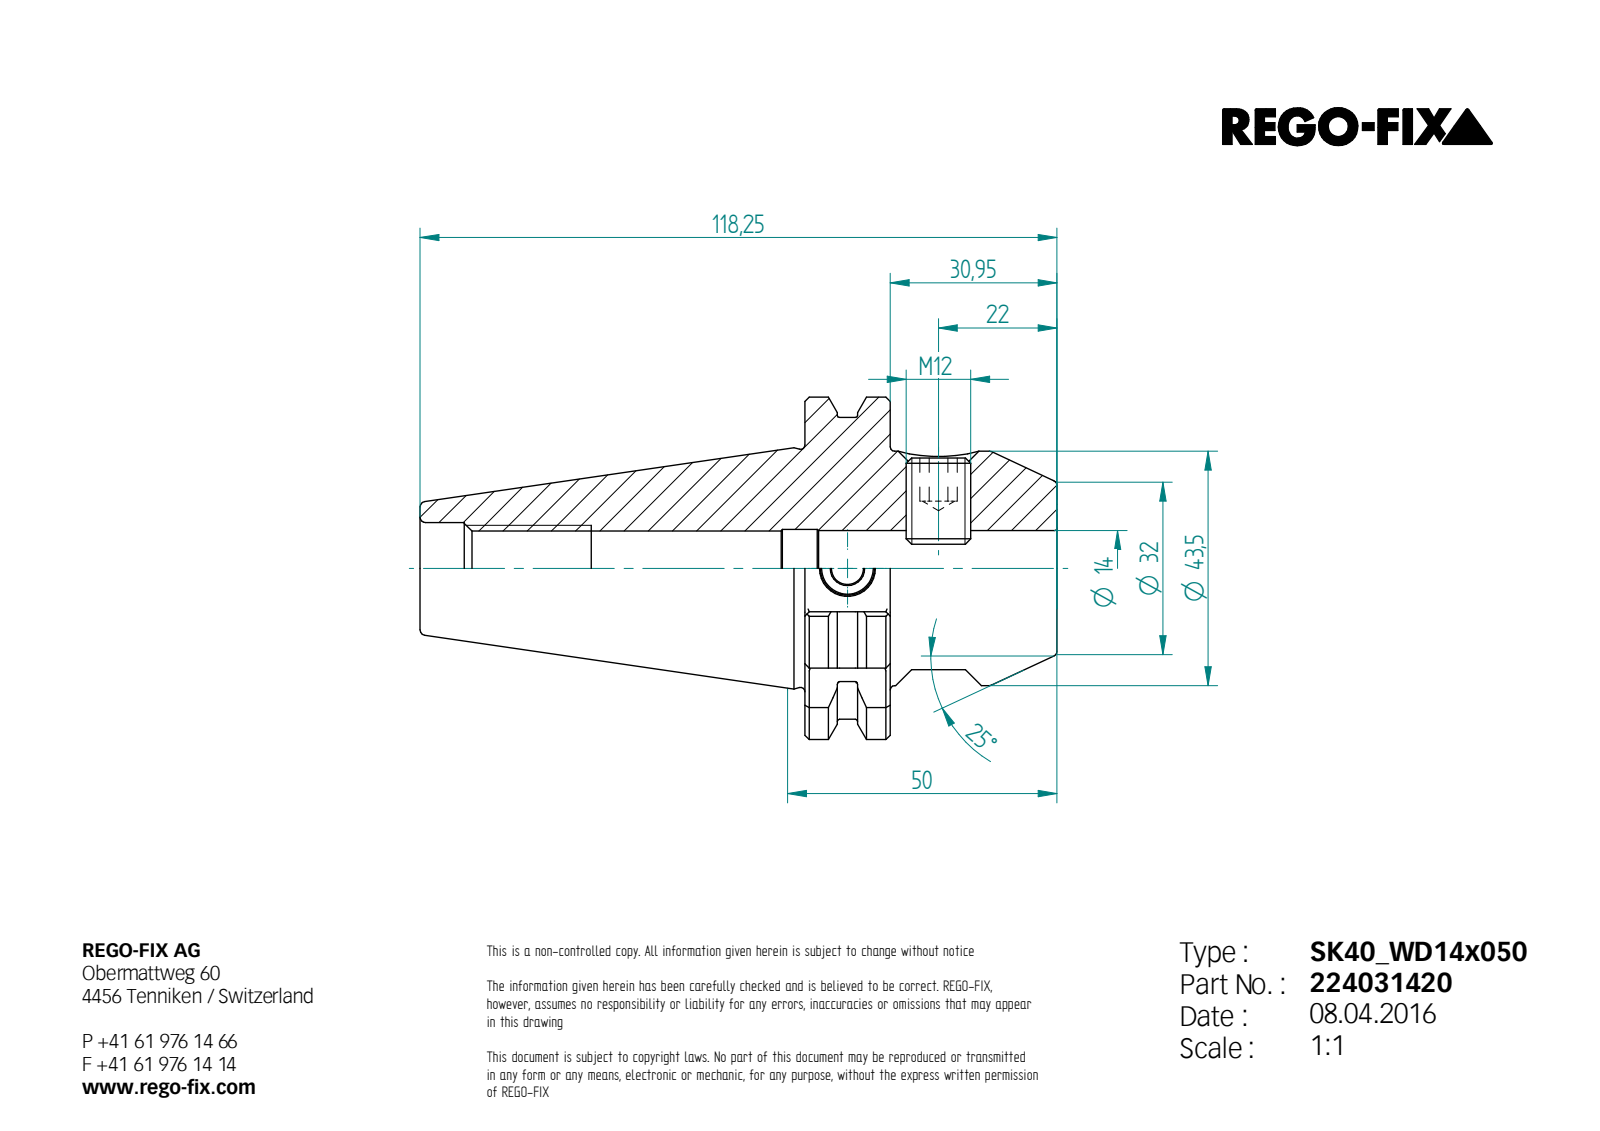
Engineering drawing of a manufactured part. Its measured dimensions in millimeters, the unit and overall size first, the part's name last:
Units: millimetres
Overall size (bounding box): 118.25 × 63.55 × 61.01
Round holes (diameter × count): ⌀6 ×1, ⌀10 ×1, ⌀10.11 ×1, ⌀13.84 ×1, ⌀14 ×1, ⌀14.5 ×1, ⌀17 ×1
Round bosses / shafts (diameter × count): ⌀43.5 ×1, ⌀12 ×1
Partial cylindrical surfaces — rounded edges, fillets, slot ends (radius × count): R0.5 ×13, R28 ×1, R31.77 ×1
Main face-to-face distances: 15.85, 46.8, 30.95, 47.3, 26.85, 10.75, 16.1, 71.45, 87.3, 118.25
Volume: 135 483 mm³ · Surface area: 26 307 mm²
Bodies: 2 solids, 130 faces (58 planar, 32 cylindrical, 40 other)
STEP written by: Unknown (AUTOMOTIVE_DESIGN)
